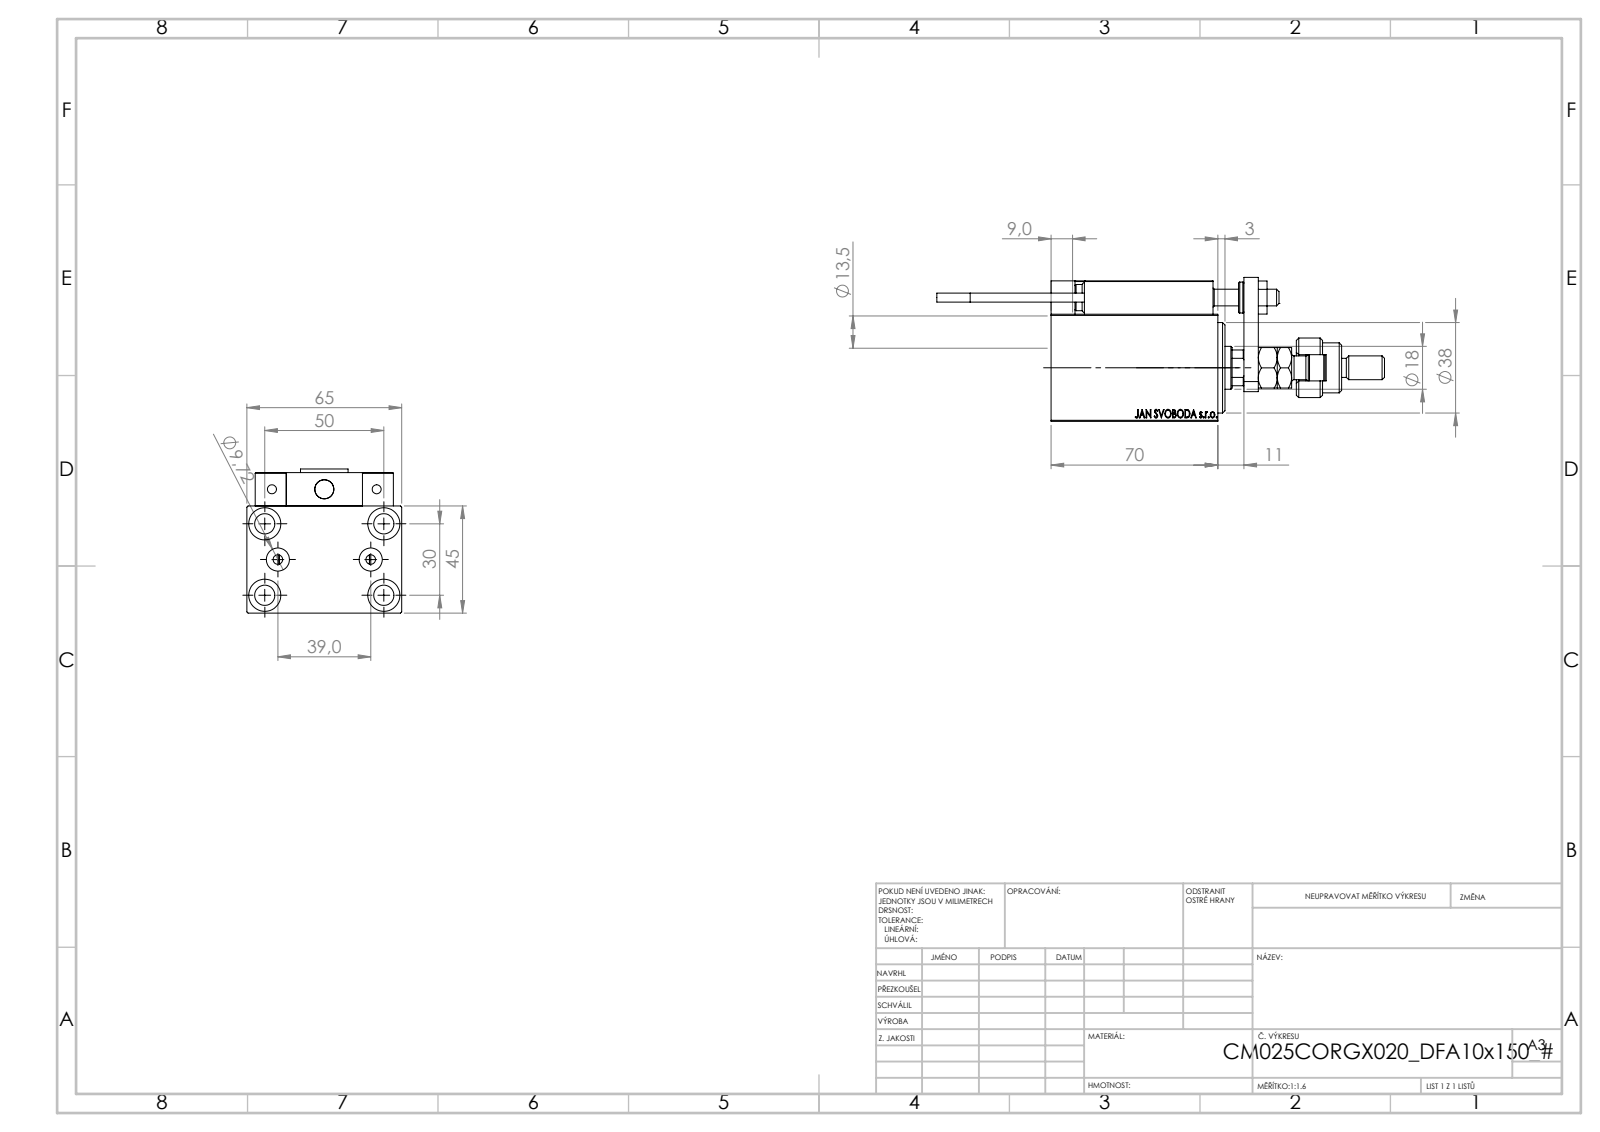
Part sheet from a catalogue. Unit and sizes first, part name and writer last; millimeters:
Units: millimetres
Overall size (bounding box): 188 × 65 × 60.5
Round holes (diameter × count): ⌀4 ×6, ⌀8 ×5, ⌀8.5 ×5, ⌀3.2 ×4, ⌀13.5 ×4, ⌀5 ×2, ⌀9.72 ×2, ⌀7 ×1, ⌀14.5 ×1, ⌀18 ×1, ⌀21.5 ×1, ⌀27 ×1
Round bosses / shafts (diameter × count): ⌀5 ×2, ⌀3.8 ×2, ⌀25 ×1, ⌀21 ×1, ⌀16 ×1, ⌀13 ×1, ⌀11 ×1, ⌀10 ×1
Partial cylindrical surfaces — rounded edges, fillets, slot ends (radius × count): R0.3 ×30, R3 ×2, R5.5 ×1, R8.5 ×1, R8.75 ×1
Main face-to-face distances: 45, 65, 59, 14, 6, 3, 19, 7, 5, 22
Hole centre spacings: 15.98, 29.15, 46.96, 11.37, 19.5, 20, 22.09, 28.9
Volume: 235 788 mm³ · Surface area: 75 405 mm²
Bodies: 25 solids, 1363 faces (588 planar, 197 cylindrical, 578 other)
Part name (STEP PRODUCT): SWITCH_X_FRONT_BACK; X_Y_DFA; V450CM_C_Body; Block (+7 more)
STEP written by: SolidWorks 2019 (CONFIG_CONTROL_DESIGN)
